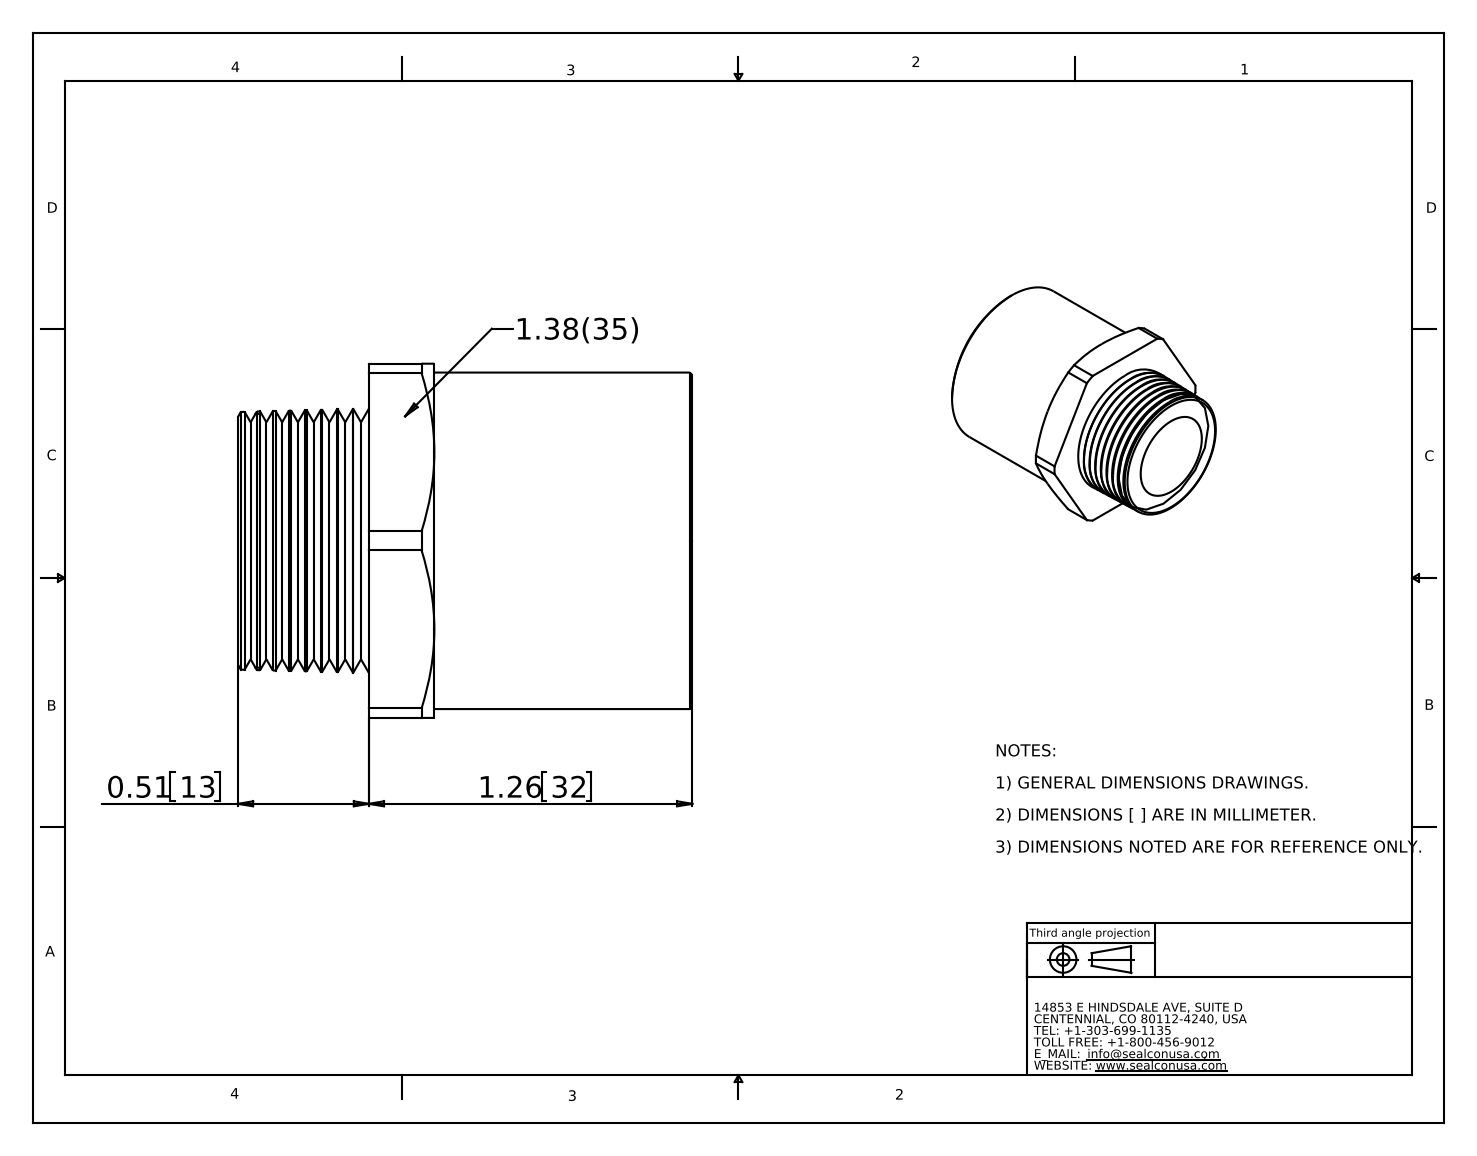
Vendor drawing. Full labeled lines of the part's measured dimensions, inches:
Part name (STEP PRODUCT): SM21NA-BK
STEP written by: SolidWorks 2007 (AUTOMOTIVE_DESIGN)
Units: inches
Bodies: 1 solid, 83 faces (11 planar, 11 cylindrical, 61 other)
Overall size (bounding box): 1.77 × 1.553 × 1.38
Volume: 1.053 in³ · Surface area: 15.55 in²
Round holes (diameter × count): ⌀1.05 ×1
Round bosses / shafts (diameter × count): ⌀1.311 ×1
Partial cylindrical surfaces — rounded edges, fillets, slot ends (radius × count): R0.776 ×1
Main face-to-face distances: 0.255, 1.38, 1.005, 1.26, 1.77, 0.765, 0.51
